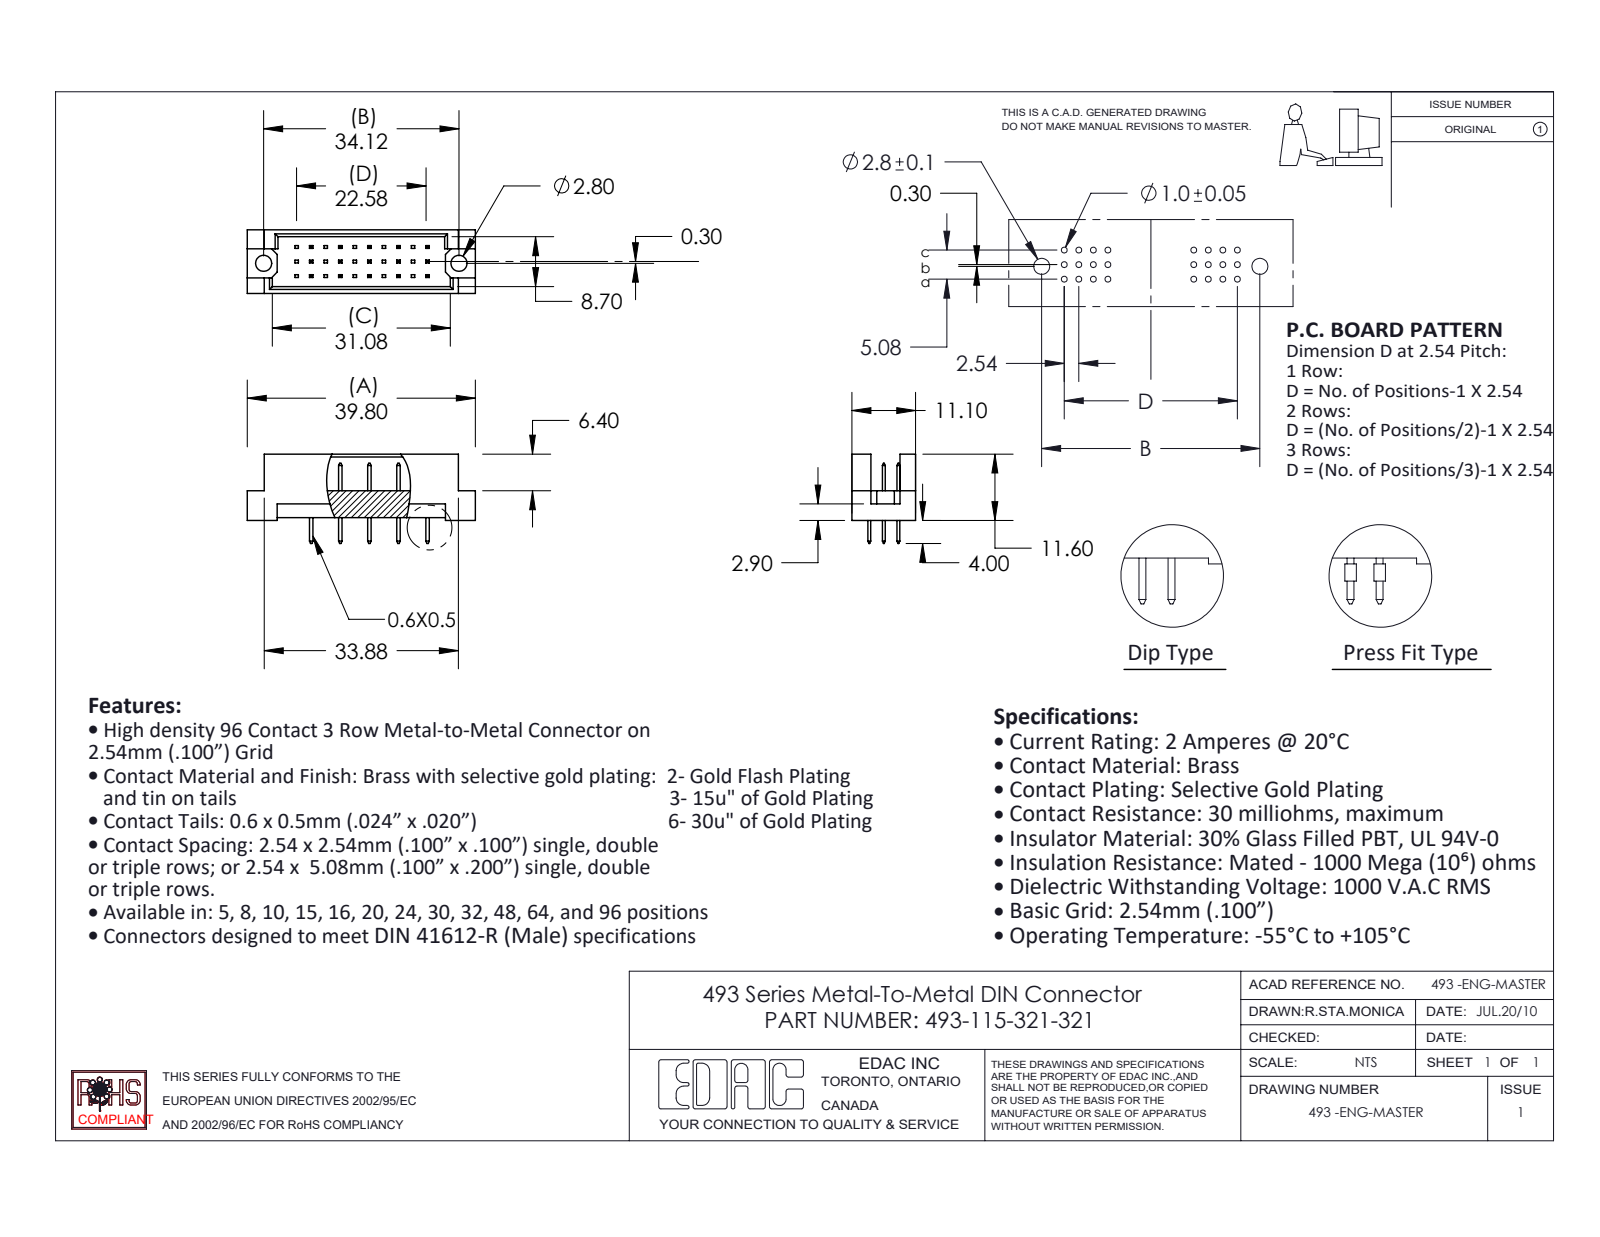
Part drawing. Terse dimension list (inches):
name: 493-115-321-321; 493 Part_30; 493-290_21
written by: SolidWorks 2020 (CONFIG_CONTROL_DESIGN)
unit: in
bodies: 16 solids, 382 faces (378 planar, 4 cylindrical, 0 other)
size: 1.567 × 0.614 × 0.437
volume: 0.149 in³; area: 4.951 in²
holes: 2× ⌀0.11
face distances: 0.047, 0.39, 0.437, 0.2, 0.02, 0.343, 0.1, 0.185, 0.4, 0.109
hole spacings: 1.343
